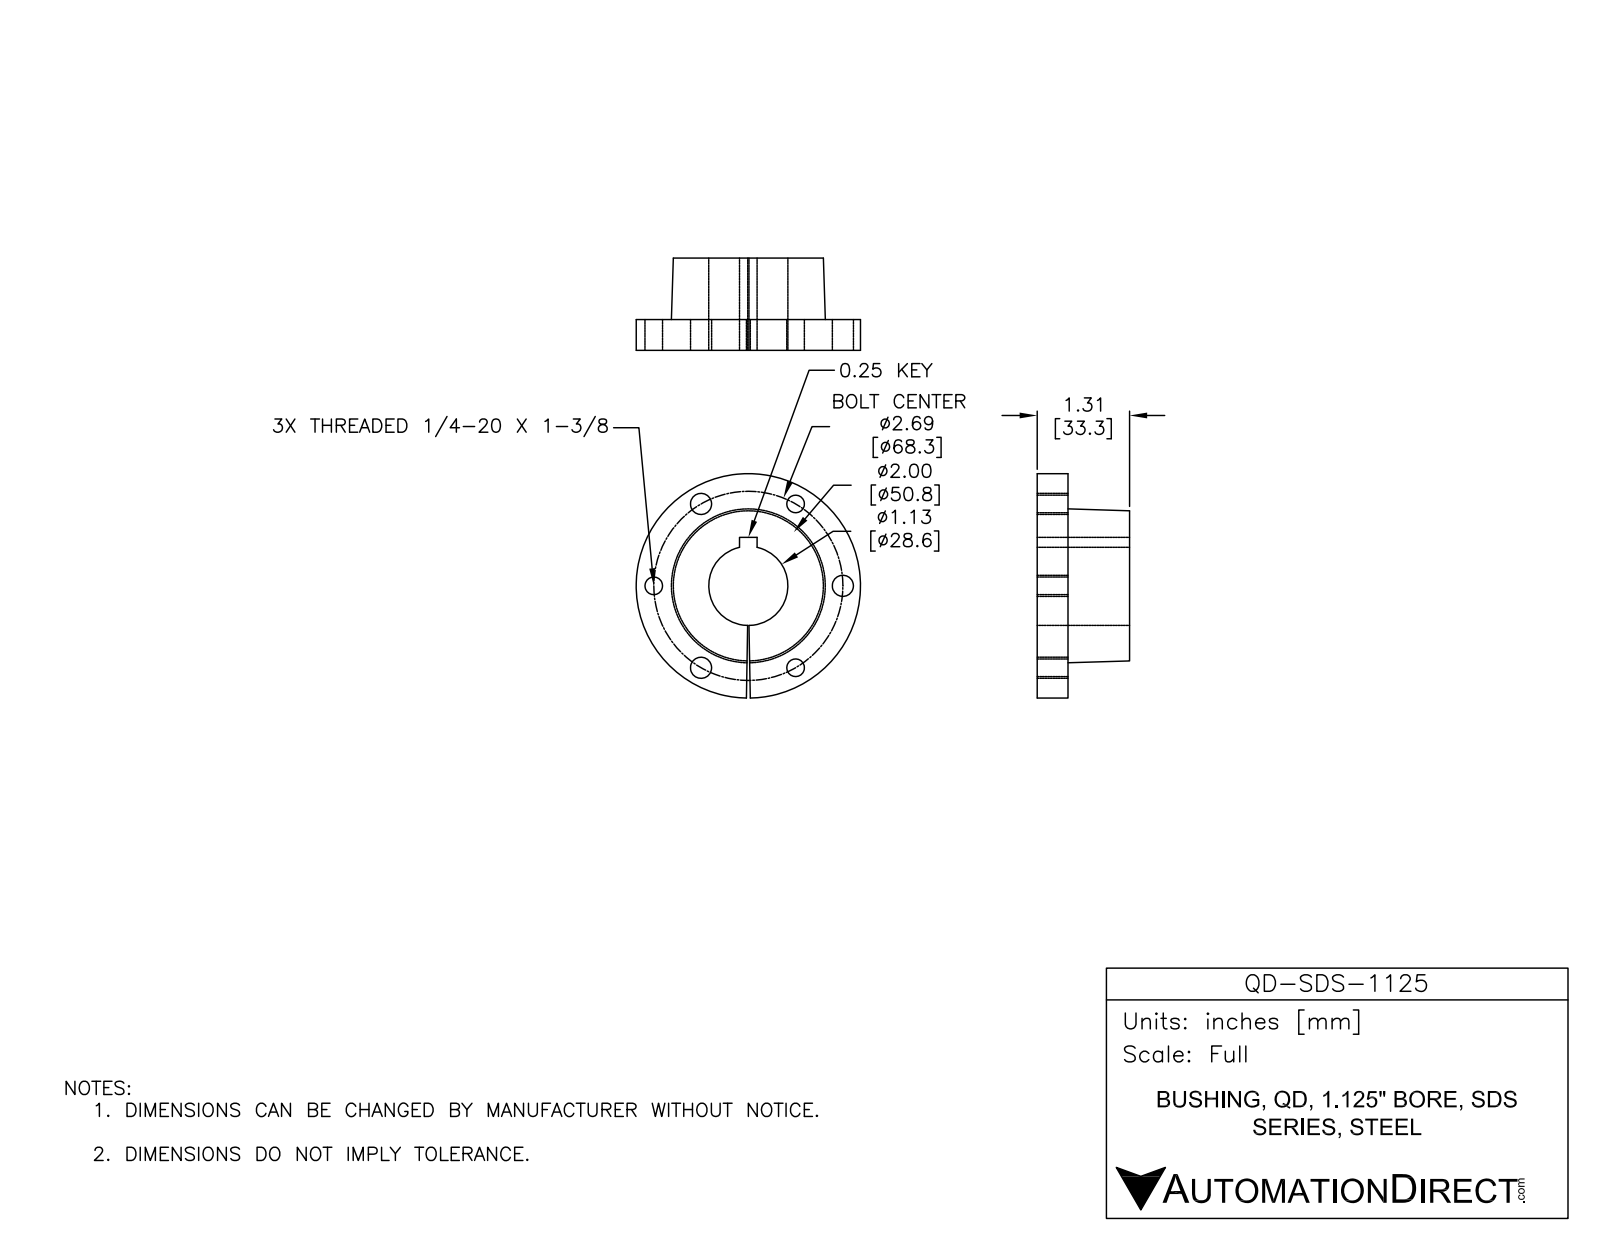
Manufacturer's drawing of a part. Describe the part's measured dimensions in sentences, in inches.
The part is named "QD-SDS-1125". Its 3-D file was written by "SolidWorks 2014 (AUTOMOTIVE_DESIGN)". It is 1 solid with 29 faces: 8 planar, 18 cylindrical and 3 other. Overall it measures 3.188 by 3.187 by 1.313 inches. Its volume is 5.164 cubic inches and its surface area 32.24 square inches. Round holes: 3 of diameter 0.25, 3 of diameter 0.3, 1 of diameter 1.125. Round bosses or shafts: 1 of diameter 3.187. The main face-to-face distances are 0.437, 1.313, 0.875, 0.25. The hole center spacings are 1.344, 2.328, 1.344, 2.688, 2.687.
